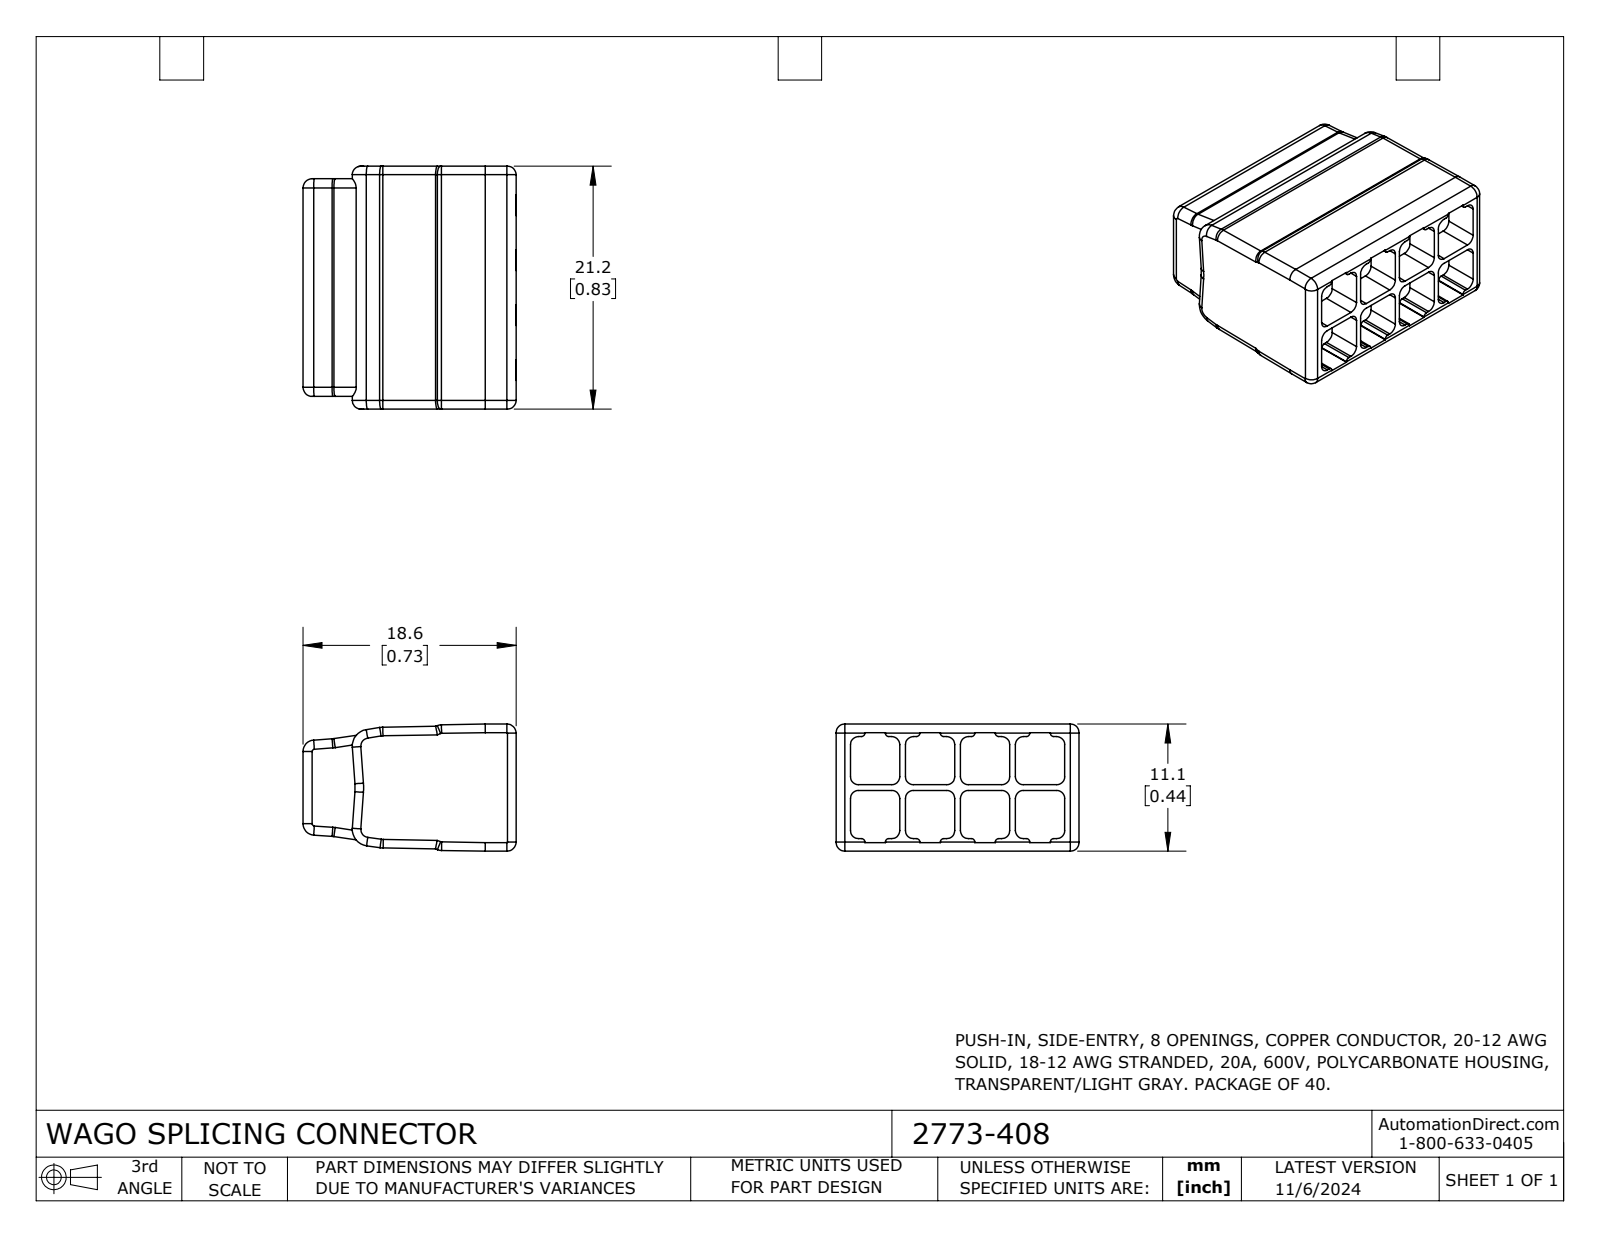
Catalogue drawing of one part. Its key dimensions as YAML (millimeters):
part_name: "2773-408"
step_written_by: "SolidWorks 2023 (CONFIG_CONTROL_DESIGN)"
units: millimeters
bodies: {solids: 1, faces: 229, planar: 101, cylindrical: 102, other: 26}
overall_size: [21.2, 18.6, 11.1]
volume: 3456
surface_area: 1907
partial_cylinders:
  - {radius: 0.7, count: 32}
  - {radius: 0.75, count: 26}
  - {radius: 0.3, count: 16}
  - {radius: 0.8, count: 12}
  - {radius: 0.6, count: 4}
  - {radius: 1, count: 4}
  - {radius: 2, count: 4}
  - {radius: 1.45, count: 2}
face_to_face_distances: [21.2, 5.3, 4.8, 15.6, 9.6, 0.5, 10.35, 5.8, 4.3, 1.1]
